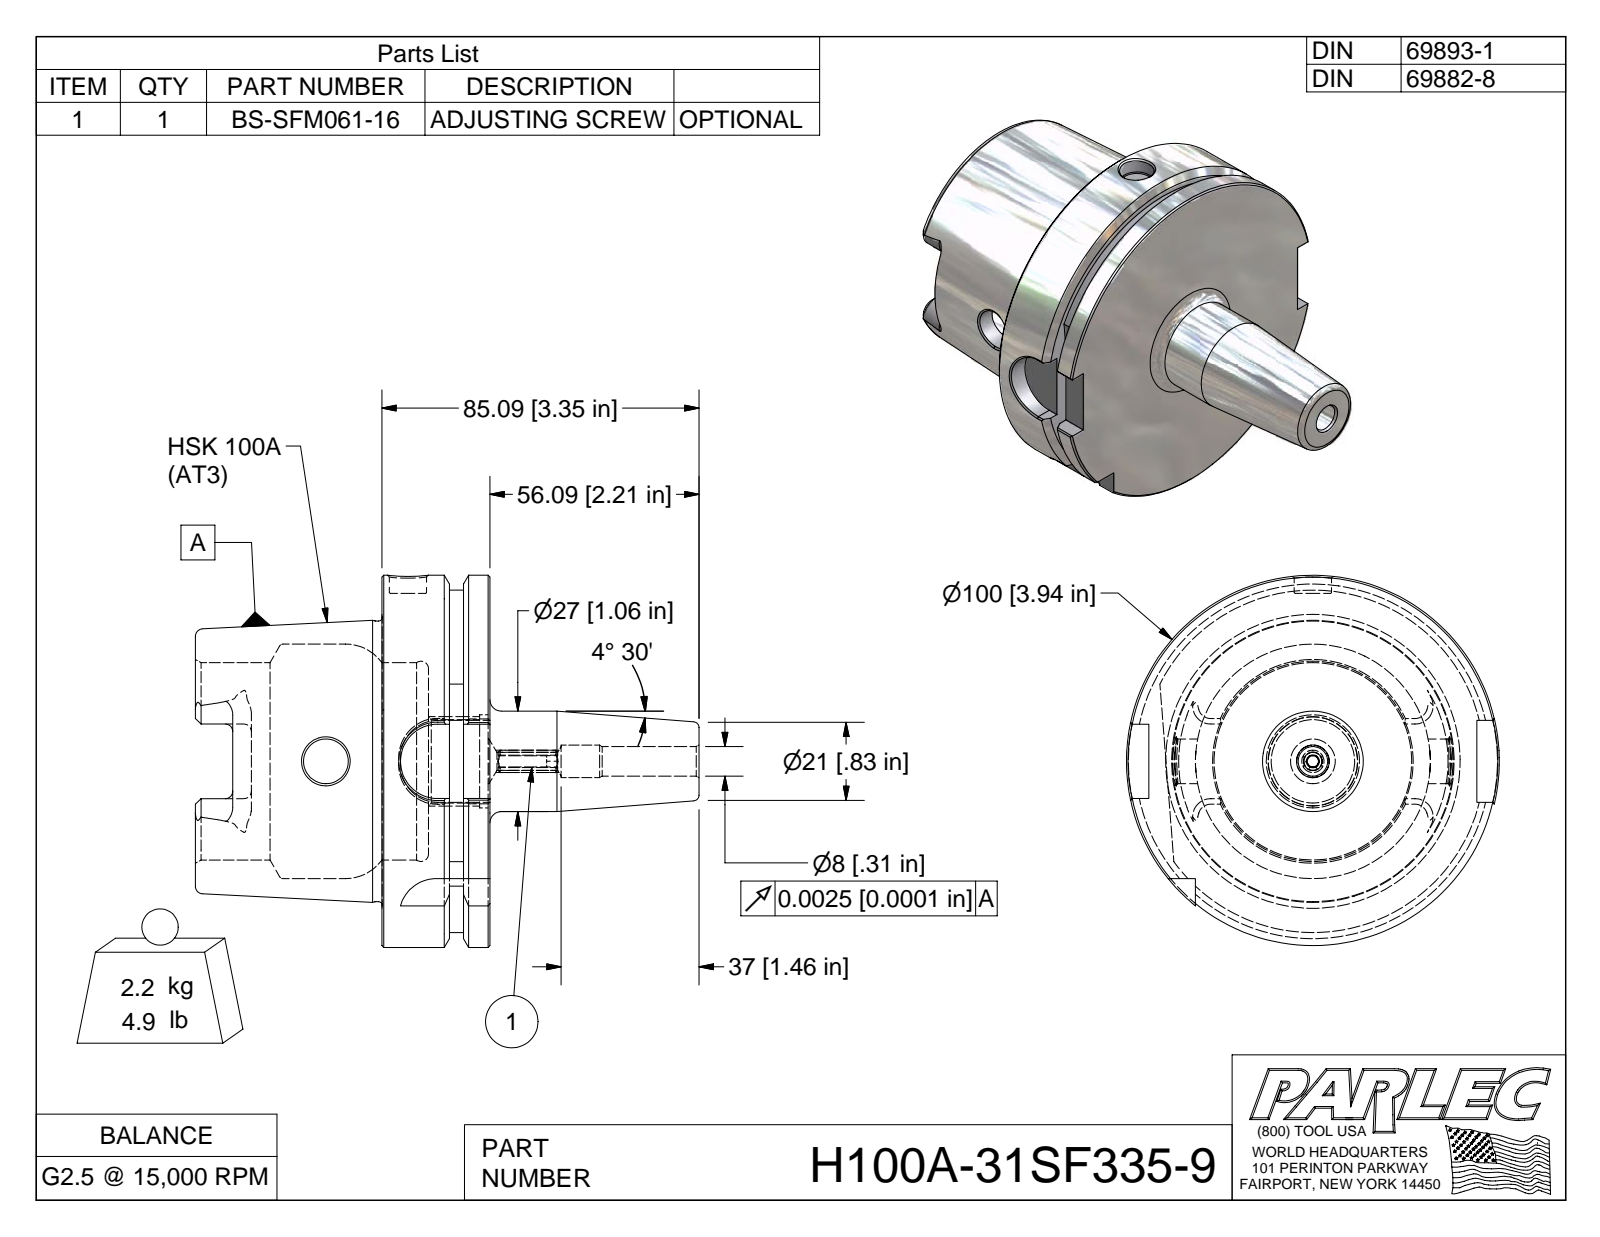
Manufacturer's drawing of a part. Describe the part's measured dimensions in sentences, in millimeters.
The part is named "H100A-31SF335-9; H100A-31SF335-9-1; BS-SFM061-16". Its 3-D file was written by "Autodesk Inventor 2009 (AUTOMOTIVE_DESIGN)". It is 2 solids with 154 faces: 49 planar, 30 cylindrical and 75 other. Overall it measures 135.1 by 100 by 100 millimeters. Its volume is 279 400 cubic millimeters and its surface area 55 780 square millimeters. Round holes: 1 of diameter 7.9, 1 of diameter 8.7, 1 of diameter 10, 1 of diameter 12, 1 of diameter 22.4, 1 of diameter 25, 1 of diameter 53, 1 of diameter 63. Round bosses or shafts: 1 of diameter 100, 1 of diameter 75.4, 1 of diameter 27. Partial cylindrical surfaces (rounded edges, fillets, slot ends): 4 of radius 10, 3 of radius 2, 2 of radius 4.9, 1 of radius 3, 1 of radius 46. The main face-to-face distances are 29, 12.5, 16.5, 50, 62.5, 79, 21.9, 68.1, 18.1, 5.6.
